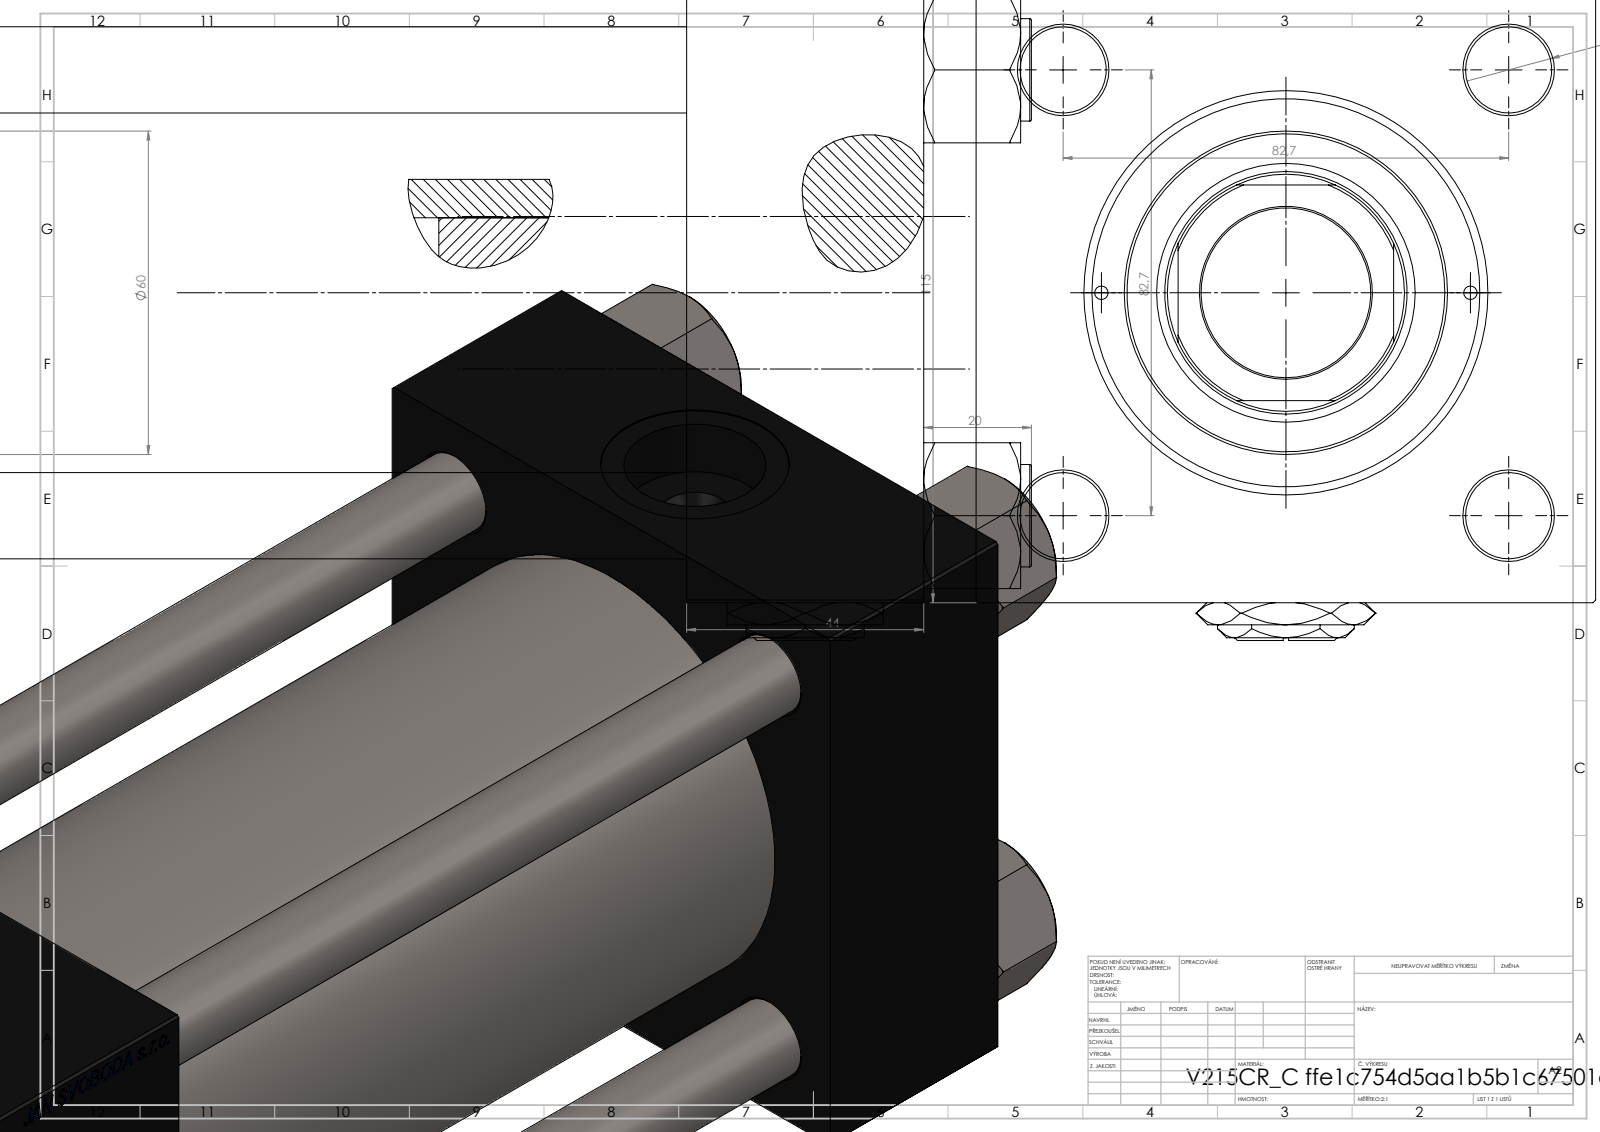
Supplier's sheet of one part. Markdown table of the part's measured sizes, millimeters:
| quantity | value |
| --- | --- |
| part name | NUT_M5_C; Zatka_pro_OIL_PORT; V215CR_VCP_C; V215_VC_A (+2 more) |
| STEP written by | SolidWorks 2019 (CONFIG_CONTROL_DESIGN) |
| units | millimeters |
| bodies | 13 solids, 1303 faces (623 planar, 102 cylindrical, 578 other) |
| overall size | 335 × 122 × 115 |
| volume | 2 138 000 mm³ |
| surface area | 371 737 mm² |
| round holes (diameter × count) | 16 × 4, 2.5 × 2, 7 × 2, 26.44 × 2, 35 × 2, 31.5 × 1, 45 × 1, 48 × 1, 61 × 1, 72 × 1, 80 × 1 |
| round bosses / shafts (diameter × count) | 19 × 4, 86 × 1, 60 × 1 |
| partial cylindrical surfaces (radius × count) | 22 × 1 |
| main face-to-face distances | 115, 44, 284, 240, 69, 215, 171, 255.3, 211.3, 40.3 |
| hole center spacings | 41.96, 58.48, 82.7, 86.17, 34.25, 116.96, 68.5, 216 |
